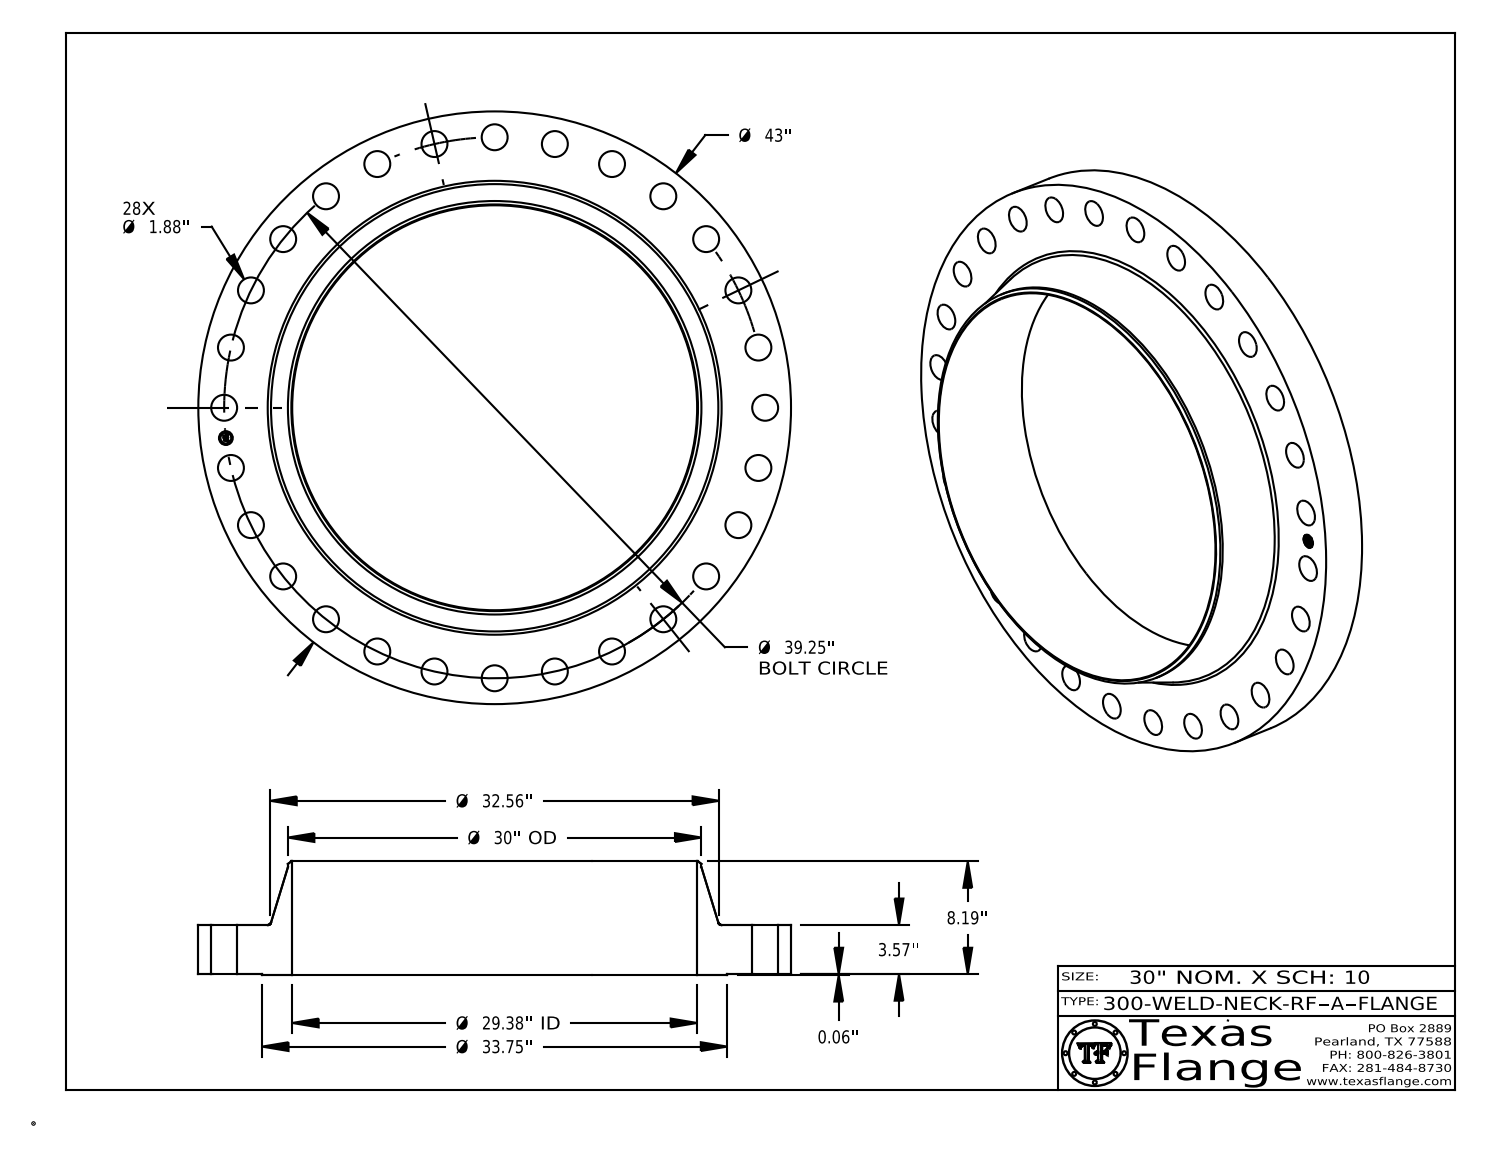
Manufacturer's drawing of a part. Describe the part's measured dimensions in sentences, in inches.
The part is named "300-WELD-NECK-RF, Series A". Its 3-D file was written by "CATIA V5 STEP AP214 (AUTOMOTIVE_DESIGN)". It is 1 solid with 459 faces: 369 planar, 84 cylindrical and 6 other. Overall it measures 43 by 43 by 8.253 inches. Its volume is 2 894 cubic inches and its surface area 3 563 square inches. Round holes: 28 of diameter 1.88, 1 of diameter 1, 1 of diameter 29.376. Round bosses or shafts: 8 of diameter 0.061, 1 of diameter 43, 1 of diameter 33.75, 1 of diameter 30, 1 of diameter 0.788. The main face-to-face distances are 3.57, 0.063, 3.633, 8.253, 8.19, 4.62, 3.618, 3.555, 0.015, 4.635. The hole center spacings are 4.394, 8.734, 12.963, 17.03, 20.882, 35.363, 24.472, 33.234.
